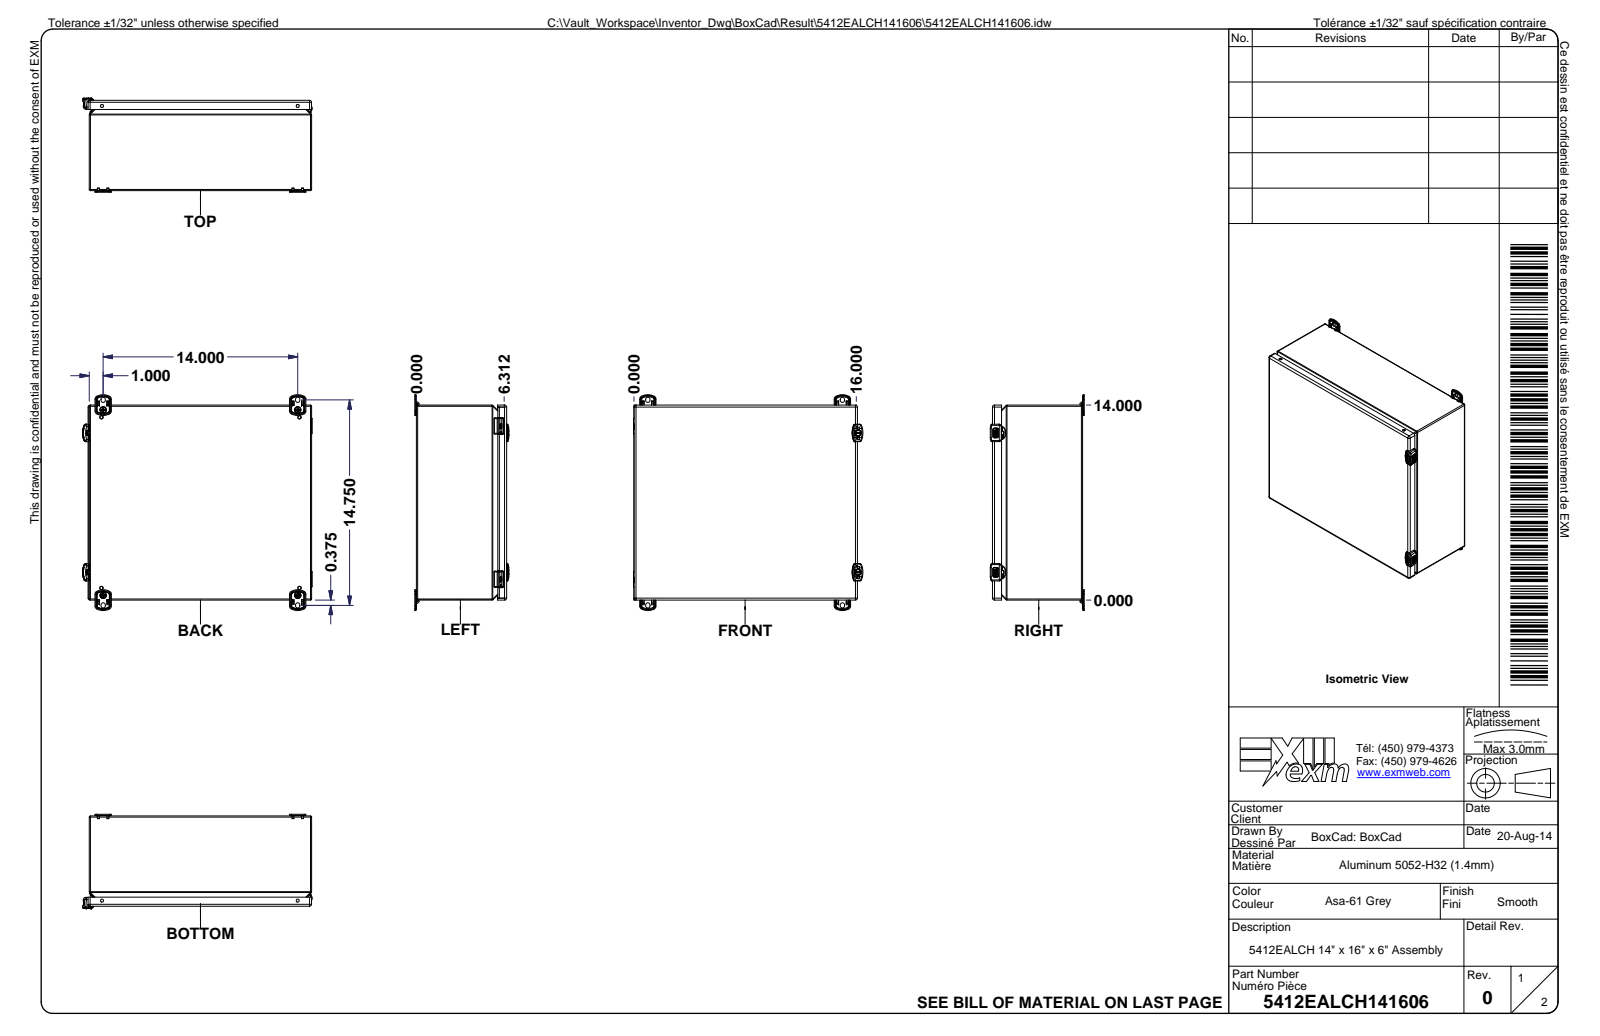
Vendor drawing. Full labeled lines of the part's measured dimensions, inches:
Part name (STEP PRODUCT): 5412EALCH141606; 5412EALCH141606B; 5412EALCH141606B-P; STK-A-70469-1 (+8 more)
STEP written by: Autodesk Inventor 2020 (AUTOMOTIVE_DESIGN)
Units: inches
Bodies: 59 solids, 8409 faces (3583 planar, 2002 cylindrical, 2824 other)
Overall size (bounding box): 16.503 × 15.496 × 6.76
Volume: 64.34 in³ · Surface area: 2 282 in²
Round holes (diameter × count): ⌀0.165 ×4, ⌀0.173 ×4, ⌀0.197 ×4, ⌀0.197 ×4, ⌀0.236 ×4, ⌀0.236 ×4, ⌀0.32 ×4, ⌀0.03 ×2, ⌀0.175 ×2, ⌀0.201 ×2, ⌀0.24 ×2, ⌀0.339 ×2
Round bosses / shafts (diameter × count): ⌀0.232 ×8, ⌀0.5 ×4, ⌀0.3 ×4, ⌀0.236 ×4, ⌀0.193 ×4, ⌀0.197 ×3, ⌀0.412 ×2, ⌀0.394 ×2
Partial cylindrical surfaces — rounded edges, fillets, slot ends (radius × count): R0.02 ×257, R0.01 ×209, R0.039 ×92, R0.004 ×64, R0.008 ×60, R0.059 ×57, R0.031 ×35, R0.005 ×33
Main face-to-face distances: 0.053, 0.053, 6.433, 6.38, 6.486, 6.433, 0.304, 0.236, 0.357, 6.076
Hole centre spacings: 0.546, 12.781, 14.135, 19.049, 12.25, 14.25, 15.293, 0.37
